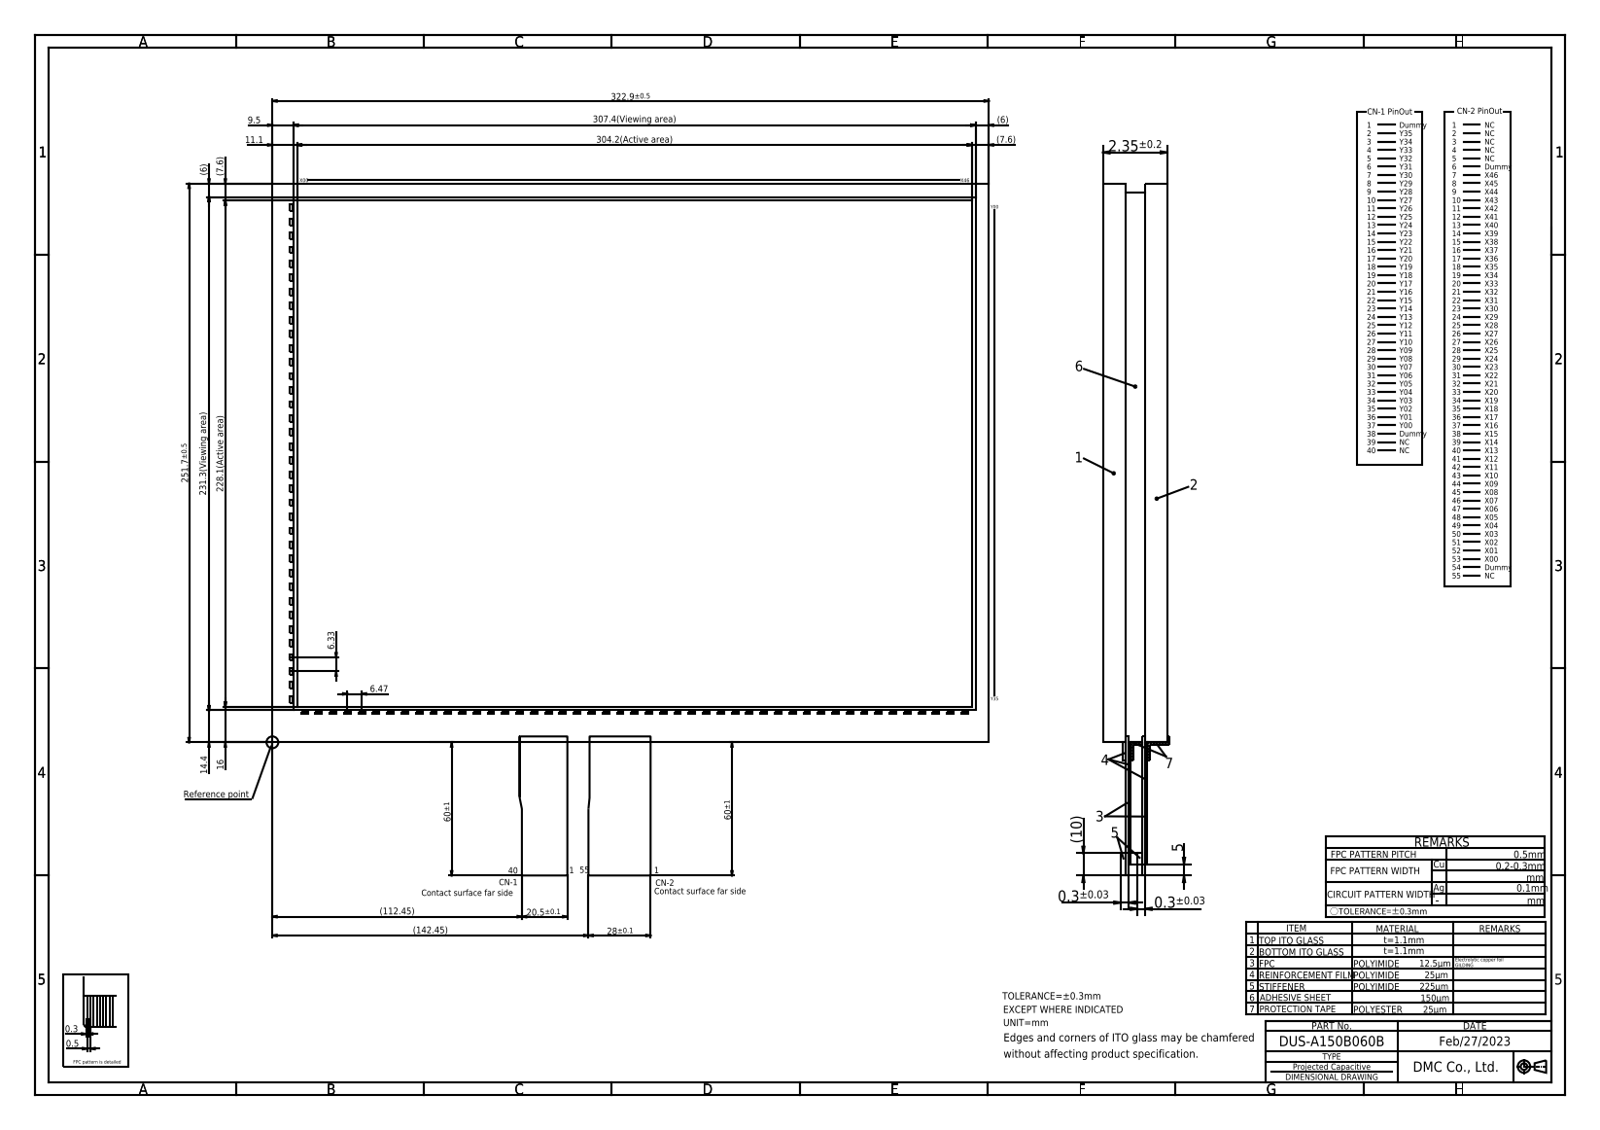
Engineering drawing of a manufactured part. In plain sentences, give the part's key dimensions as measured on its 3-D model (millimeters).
The part is named "DUS-A150B060B". Its 3-D file was written by "Autodesk Inventor 2020 (CONFIG_CONTROL_DESIGN)". It is 1 solid with 422 faces: 418 planar, 4 cylindrical and 0 other. Overall it measures 452.06 by 362.04 by 2.35 millimeters. Its volume is 191 235 cubic millimeters and its surface area 171 382 square millimeters. Partial cylindrical surfaces (rounded edges, fillets, slot ends): 4 of radius 0.2. The main face-to-face distances are 2.35, 1.1, 1.15, 1.2, 1.25, 1, 2.25, 251.7, 322.9, 0.8.
